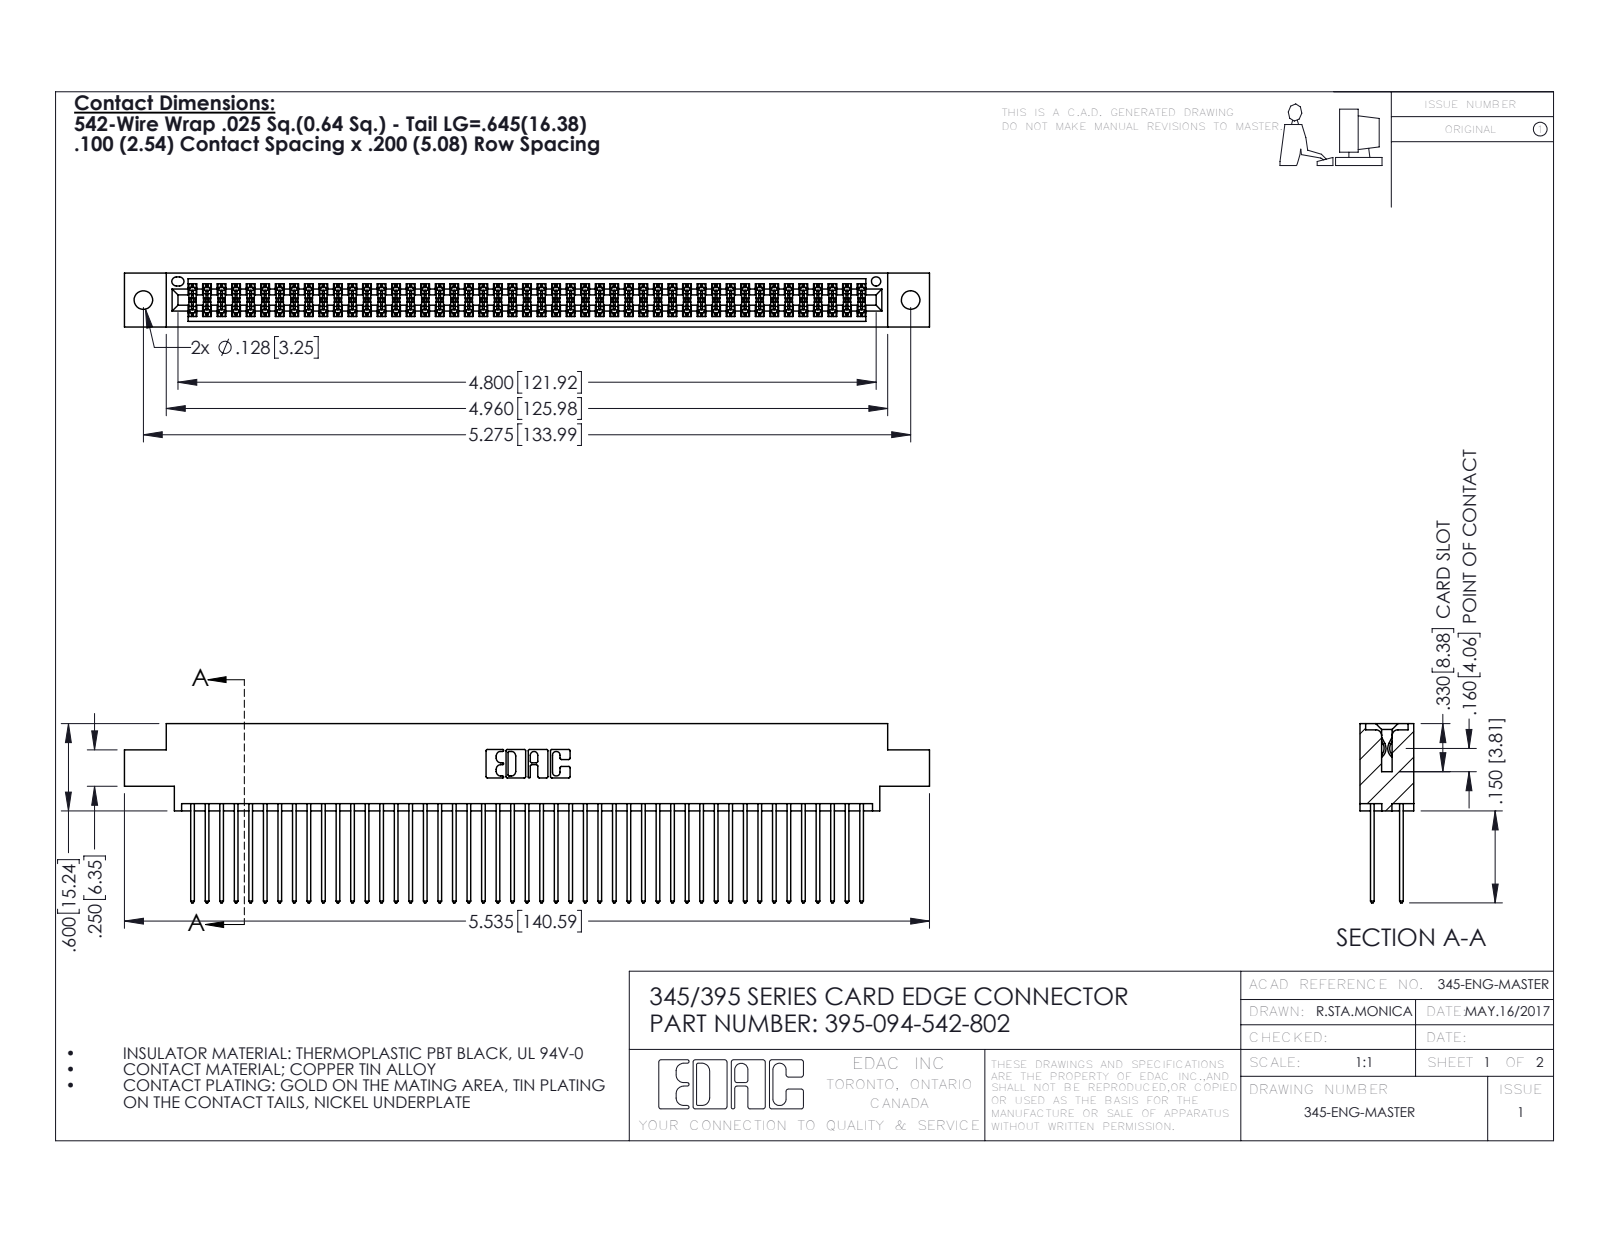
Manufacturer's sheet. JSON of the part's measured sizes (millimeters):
{"part_name": "395-094-542-802; 345-292-001_345-293-142; 345 Part_0.170 Offset - 0.128 Dia", "step_written_by": "SolidWorks 2016 (CONFIG_CONTROL_DESIGN)", "units": "millimeters", "bodies": {"solids": 95, "faces": 4830, "planar": 3186, "cylindrical": 1644, "other": 0}, "overall_size": [140.6, 31.3, 9.4], "volume_mm3": 14000, "surface_area_mm2": 22700, "round_holes": [[3.3, 2], [1.6, 1]], "partial_cylinders_radius": [[0.2, 141], [0.3, 94], [0.3, 22], [0.2, 6], [0.8, 6], [0.7, 3], [0.4, 2], [0.5, 2]], "face_to_face_distances": [7.6, 1.8, 5.1, 2.5, 6.9, 0.6, 9.4, 5.7, 4.4, 3.8], "hole_center_spacings": [6.9, 128, 134]}
